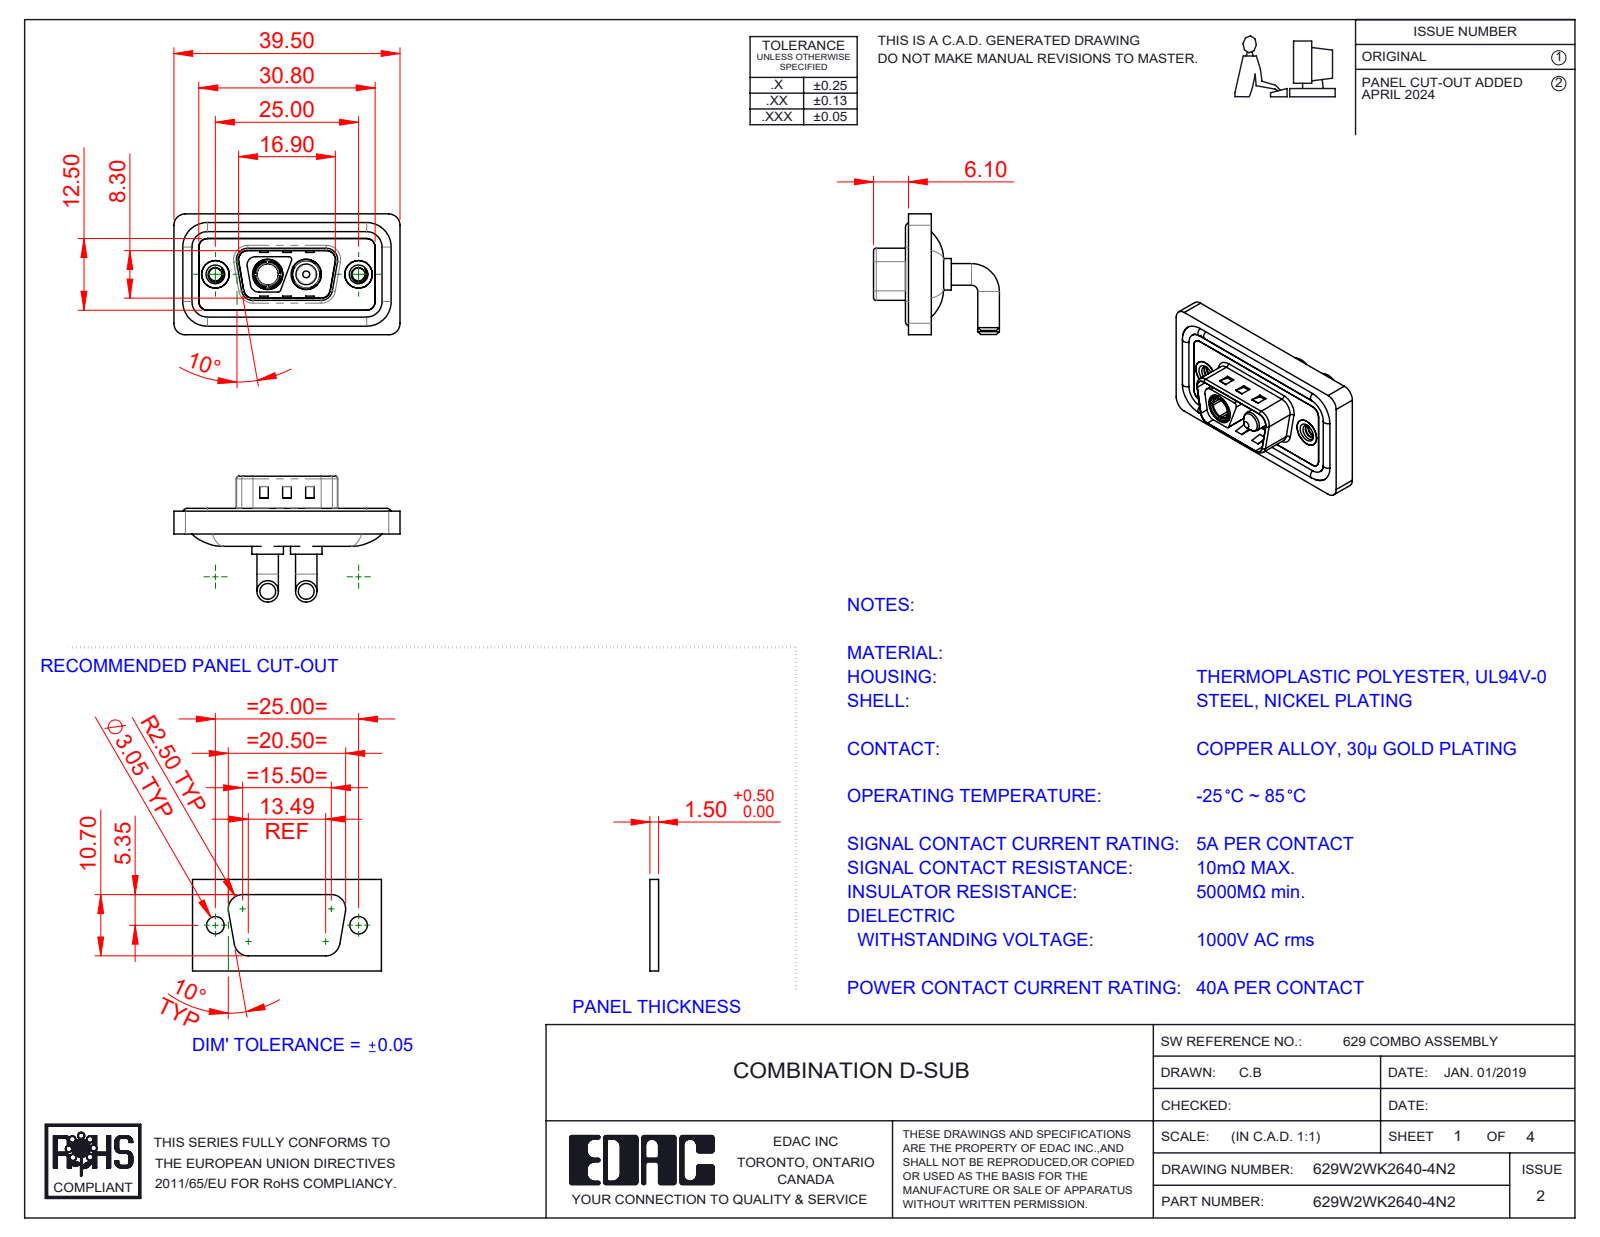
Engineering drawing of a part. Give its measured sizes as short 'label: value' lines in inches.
name: 629Combo Shell Front_09 Contacts; 629Combo Housing_2WK2; 629W2WK2640-4N2; 629Combo Shell Rear_09 Contacts (+4 more)
written by: SolidWorks 2023 (CONFIG_CONTROL_DESIGN)
unit: in
bodies: 11 solids, 542 faces (189 planar, 231 cylindrical, 122 other)
size: 1.555 × 0.865 × 0.831
volume: 0.295 in³; area: 11.81 in²
holes: 2× ⌀0.089, 2× ⌀0.157, 2× ⌀0.189, 2× ⌀0.191, 2× ⌀0.197, 2× ⌀0.209, 1× ⌀0.146
bosses: 4× ⌀0.148, 4× ⌀0.063, 2× ⌀0.217, 2× ⌀0.205, 2× ⌀0.193, 2× ⌀0.187, 1× ⌀0.195, 1× ⌀0.142
rounds: 20× R0.059, 18× R0.079, 10× R0.02, 8× R0.063, 4× R0.01, 4× R0.024, 4× R0.026, 4× R0.035
face distances: 0.016, 0.114, 0.043, 0.031, 0.083, 0.098, 0.122, 0.063, 0.177, 0.059
hole spacings: 0.36, 0.624, 0.265, 0.984
